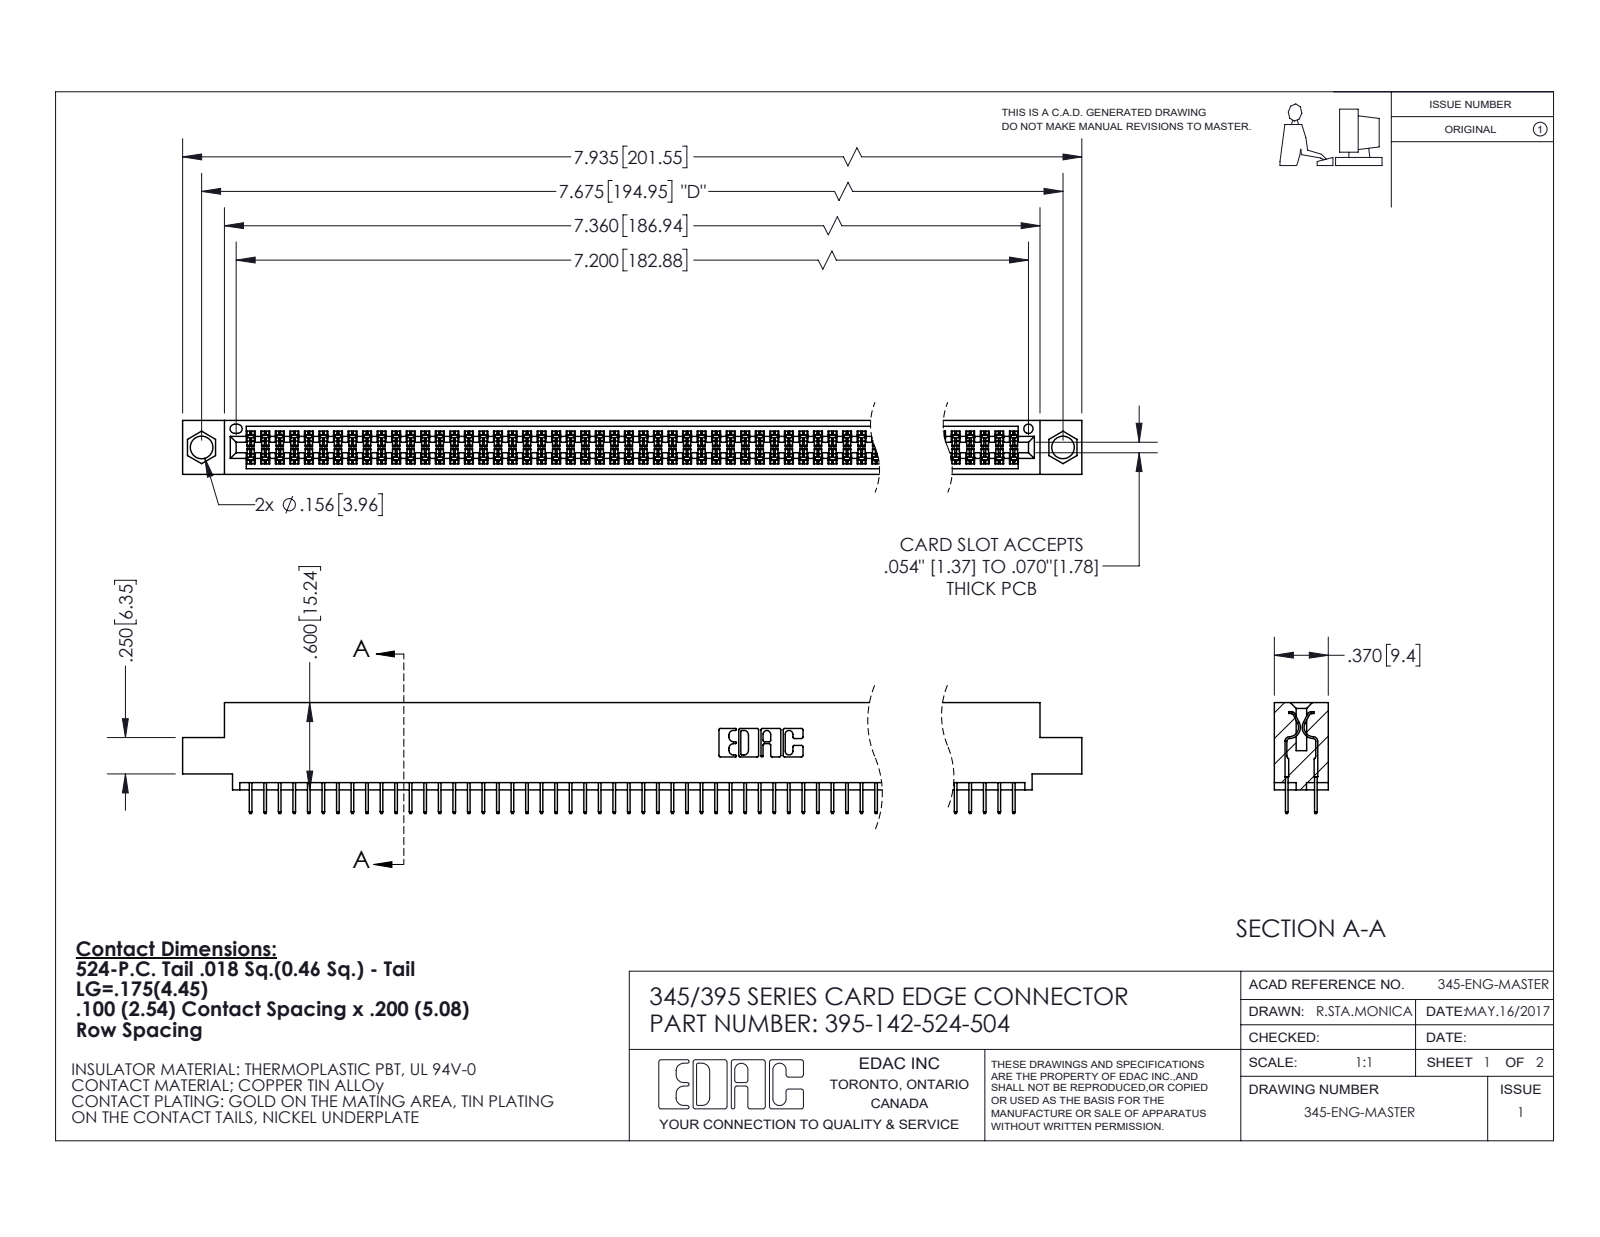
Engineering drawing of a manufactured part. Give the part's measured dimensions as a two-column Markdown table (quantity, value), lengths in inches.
| quantity | value |
| --- | --- |
| part name | 395-142-524-504; 345 Part_0.110 Offset - 0.156 Dia-TI; 345-292-001_345-293-124 |
| STEP written by | SolidWorks 2020 (CONFIG_CONTROL_DESIGN) |
| units | inches |
| bodies | 143 solids, 7812 faces (5636 planar, 2176 cylindrical, 0 other) |
| overall size | 7.935 × 0.762 × 0.37 |
| volume | 1.187 in³ |
| surface area | 44.48 in² |
| round holes (diameter × count) | 0.156 × 2, 0.064 × 1 |
| partial cylindrical surfaces (radius × count) | 0.006 × 213, 0.01 × 22, 0.007 × 6, 0.031 × 6, 0.026 × 3, 0.014 × 2, 0.019 × 2, 0.022 × 2 |
| main face-to-face distances | 0.072, 0.298, 0.2, 0.37, 0.098, 0.272, 0.025, 0.225, 0.072, 0.175 |
| hole center spacings | 0.27, 7.439, 7.675 |
